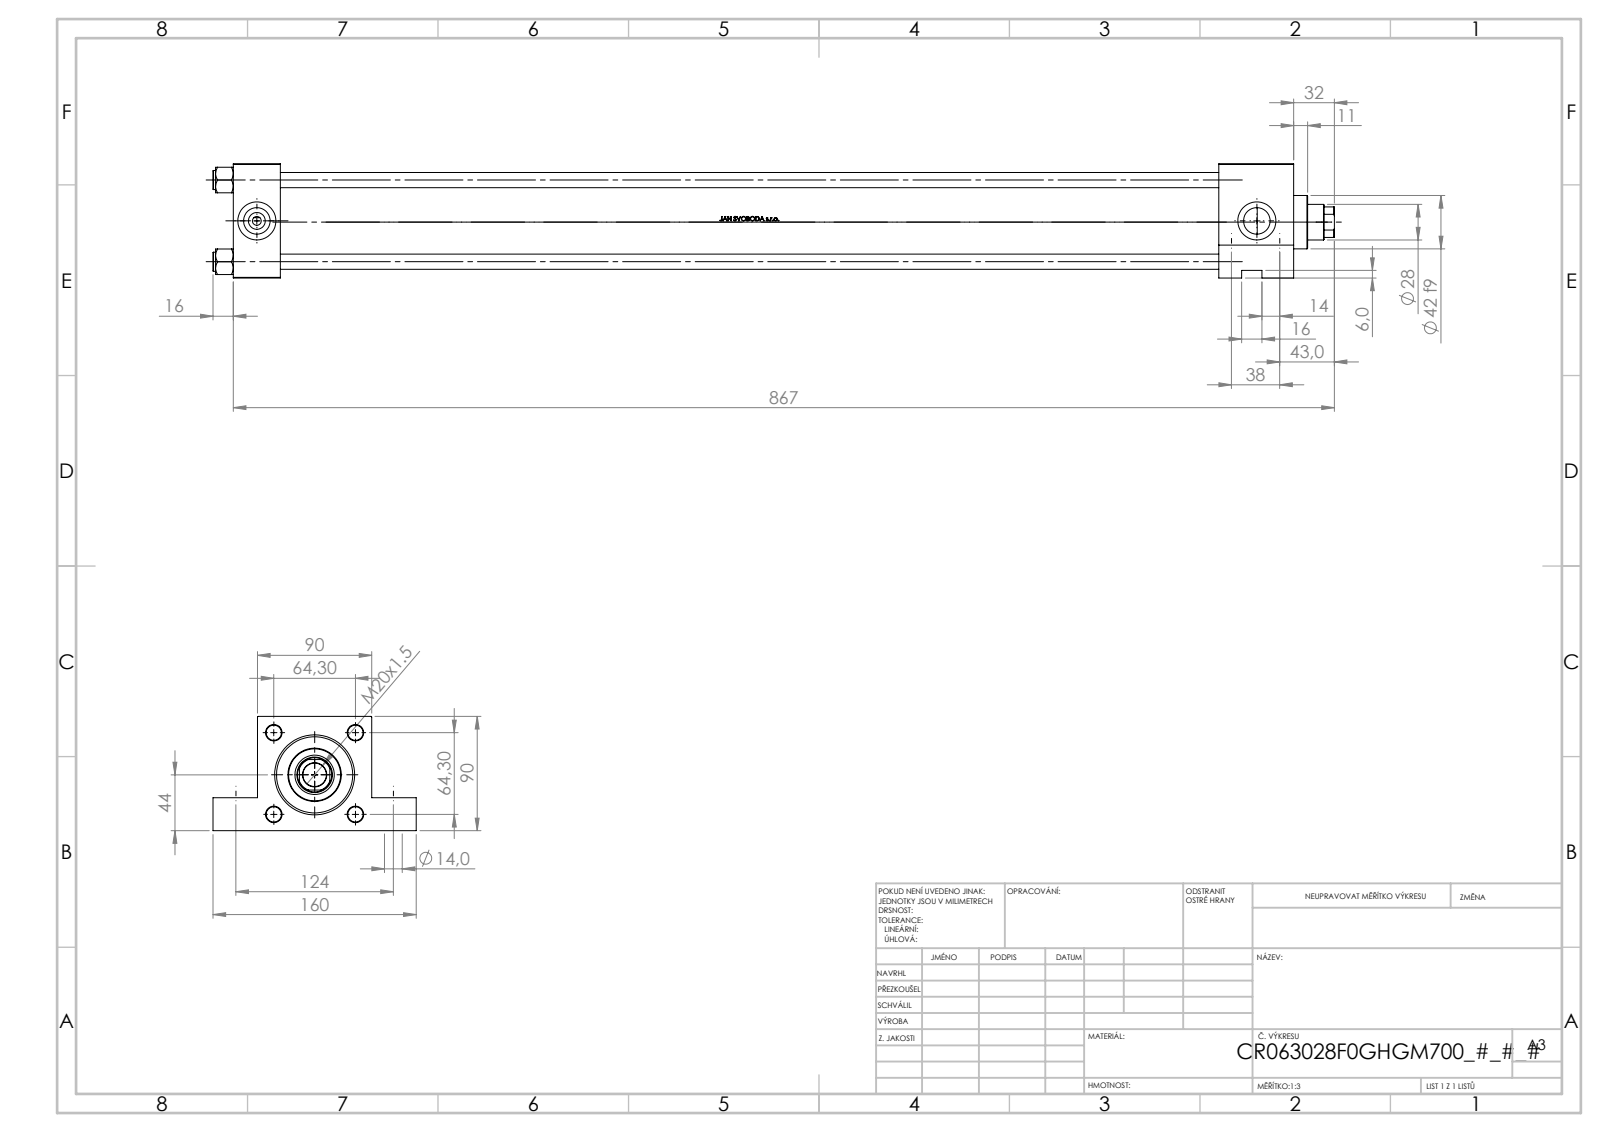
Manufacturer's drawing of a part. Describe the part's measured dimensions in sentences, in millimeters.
The part is named "V215CR_F_TYCINKA; V215_VC_A; V215CR_F_Body; NUT_M5_F (+1 more)". Its 3-D file was written by "SolidWorks 2019 (CONFIG_CONTROL_DESIGN)". It is 11 solids with 1103 faces: 437 planar, 126 cylindrical and 540 other. Overall it measures 883 by 160 by 90 millimeters. Its volume is 2 179 000 cubic millimeters and its surface area 638 134 square millimeters. Round holes: 4 of diameter 12, 4 of diameter 14, 2 of diameter 7, 2 of diameter 20.96, 2 of diameter 30, 1 of diameter 18.5, 1 of diameter 28, 1 of diameter 31, 1 of diameter 50, 1 of diameter 60, 1 of diameter 63. Round bosses or shafts: 4 of diameter 15, 1 of diameter 69, 1 of diameter 42. Partial cylindrical surfaces (rounded edges, fillets, slot ends): 1 of radius 13.5. The main face-to-face distances are 90, 37, 835, 798, 776, 739, 59, 26, 64, 806.3. The hole center spacings are 64.3, 38, 44.77, 46.18, 90.93, 124, 129.69, 787.5.
